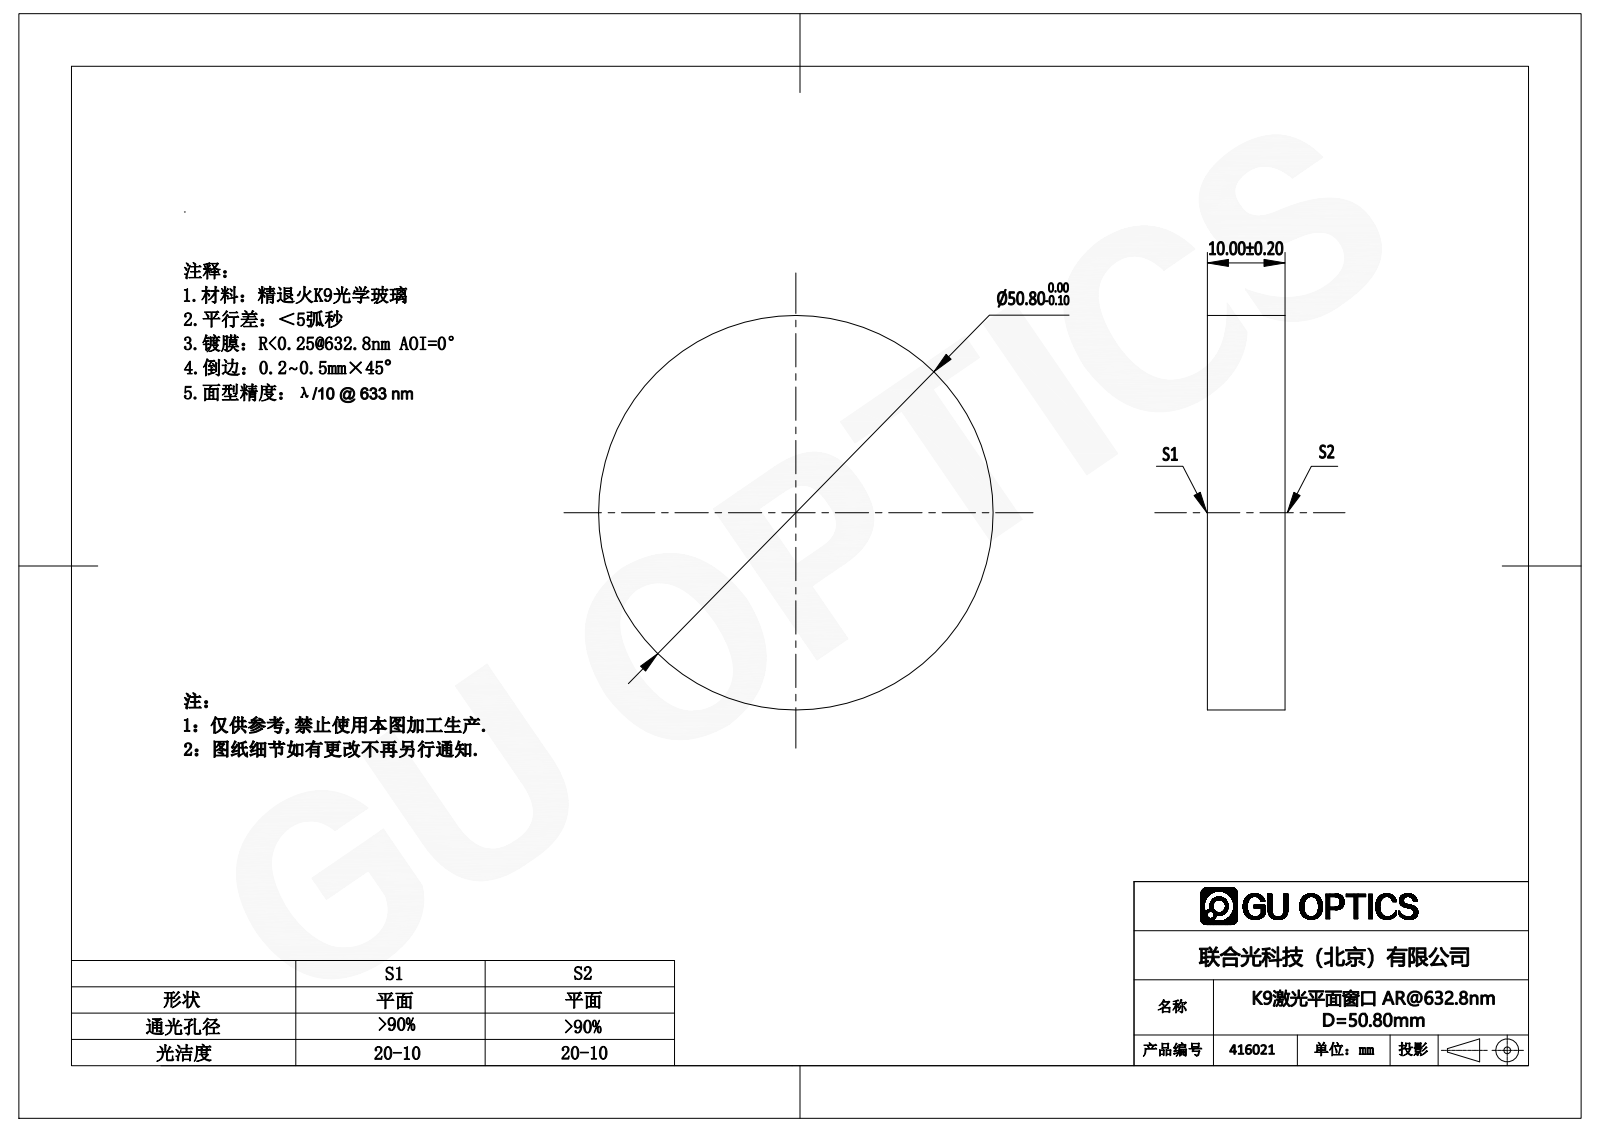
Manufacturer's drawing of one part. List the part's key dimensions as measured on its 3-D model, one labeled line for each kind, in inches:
Part name (STEP PRODUCT): 416010
STEP written by: SolidWorks 2016 (CONFIG_CONTROL_DESIGN)
Units: inches
Bodies: 1 solid, 4 faces (2 planar, 2 cylindrical, 0 other)
Overall size (bounding box): 2 × 2 × 0.394
Volume: 1.237 in³ · Surface area: 8.758 in²
Round bosses / shafts (diameter × count): ⌀2 ×1
Main face-to-face distances: 0.394
